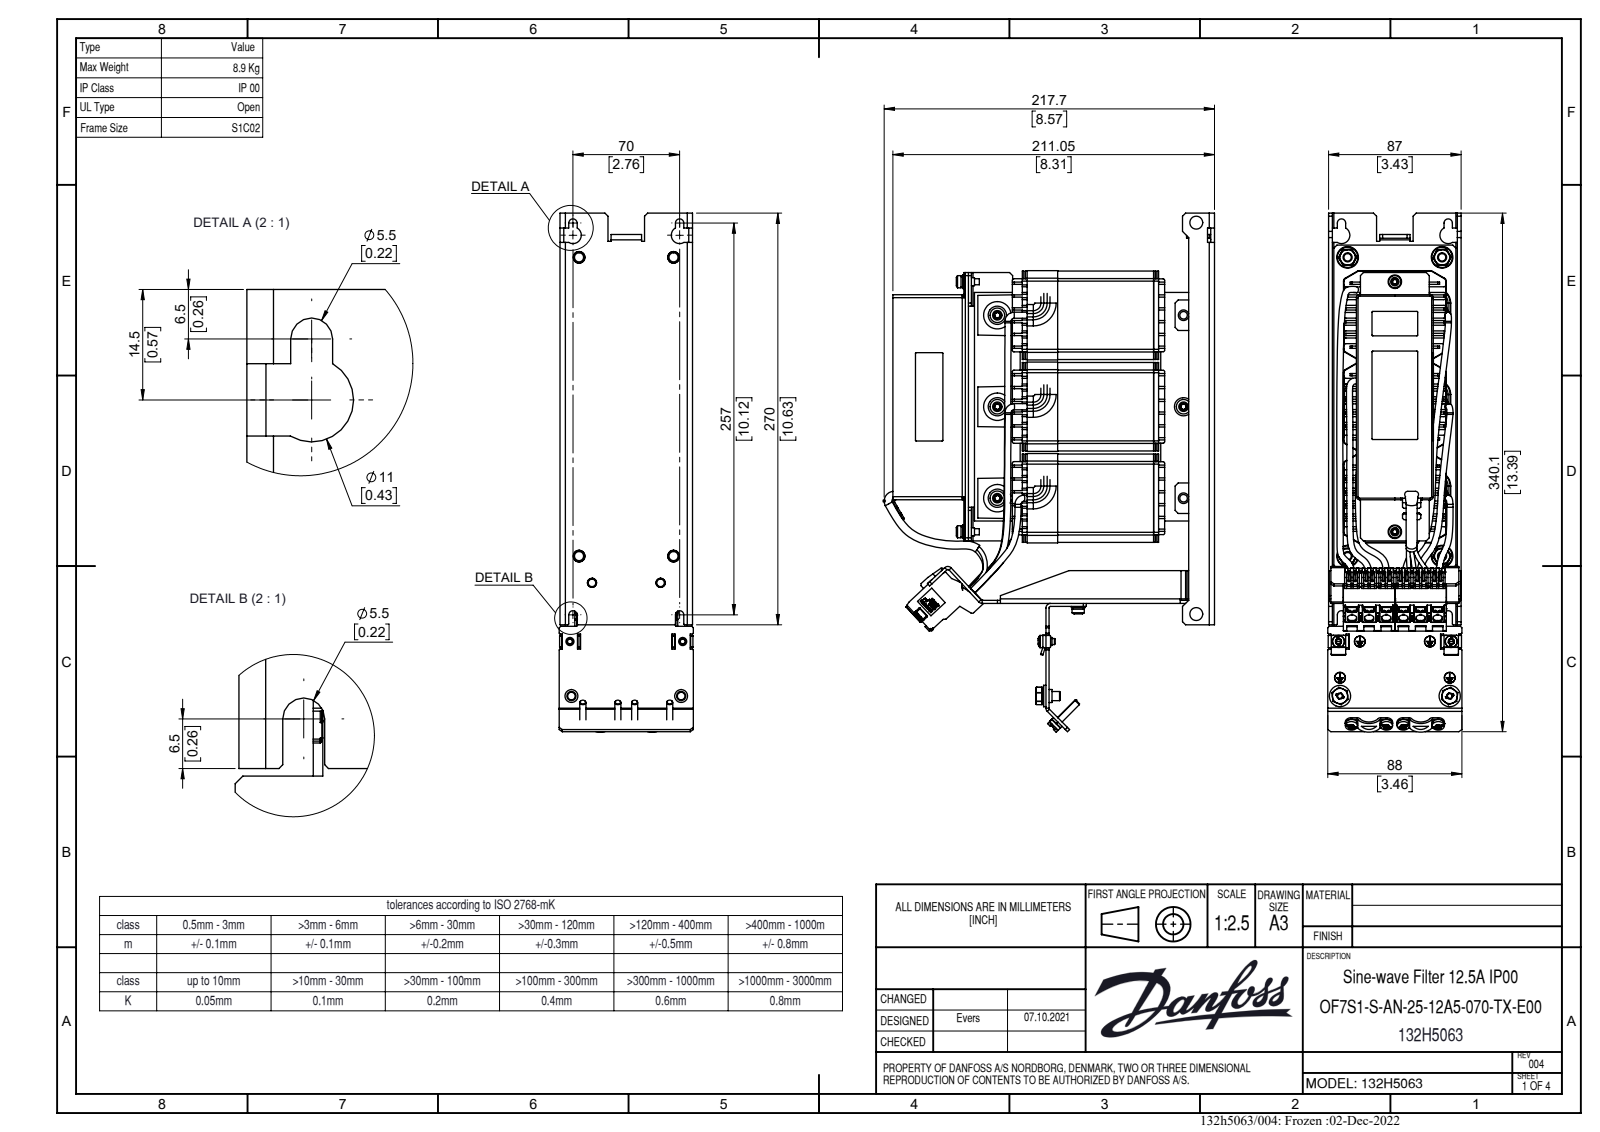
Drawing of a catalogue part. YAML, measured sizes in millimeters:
part_name: "132H4239_PART"
step_written_by: "CREO PARAMETRIC BY PTC INC, 2020342 (CONFIG_CONTROL_DESIGN)"
units: millimeters
bodies: {solids: 7, faces: 1682, planar: 1394, cylindrical: 288, other: 0}
overall_size: [340.5, 211.07, 88]
volume: 1905000
surface_area: 348697
round_holes:
  - {diameter: 4.5, count: 6}
  - {diameter: 6.4, count: 6}
  - {diameter: 2.85, count: 4}
  - {diameter: 6, count: 4}
  - {diameter: 7.15, count: 4}
  - {diameter: 3.3, count: 3}
  - {diameter: 2.88, count: 2}
  - {diameter: 3.04, count: 2}
  - {diameter: 3.95, count: 2}
  - {diameter: 4, count: 2}
  - {diameter: 5, count: 2}
  - {diameter: 8.5, count: 2}
round_bosses_or_shafts:
  - {diameter: 7, count: 10}
  - {diameter: 8, count: 9}
  - {diameter: 9.5, count: 6}
  - {diameter: 6, count: 6}
  - {diameter: 5, count: 6}
  - {diameter: 8.9, count: 4}
  - {diameter: 4, count: 4}
  - {diameter: 3.7, count: 4}
partial_cylinders:
  - {radius: 1, count: 5}
  - {radius: 0.5, count: 4}
  - {radius: 2.75, count: 4}
  - {radius: 2, count: 3}
  - {radius: 3, count: 3}
  - {radius: 2.65, count: 2}
  - {radius: 5.5, count: 2}
  - {radius: 7.5, count: 2}
face_to_face_distances: [2, 4.5, 58.6, 1.4, 60, 49.45, 9.45, 2.5, 9.8, 58.9]
hole_center_spacings: [60, 34.89, 136.14, 182.65, 122.2, 11.25, 12, 19.46]
